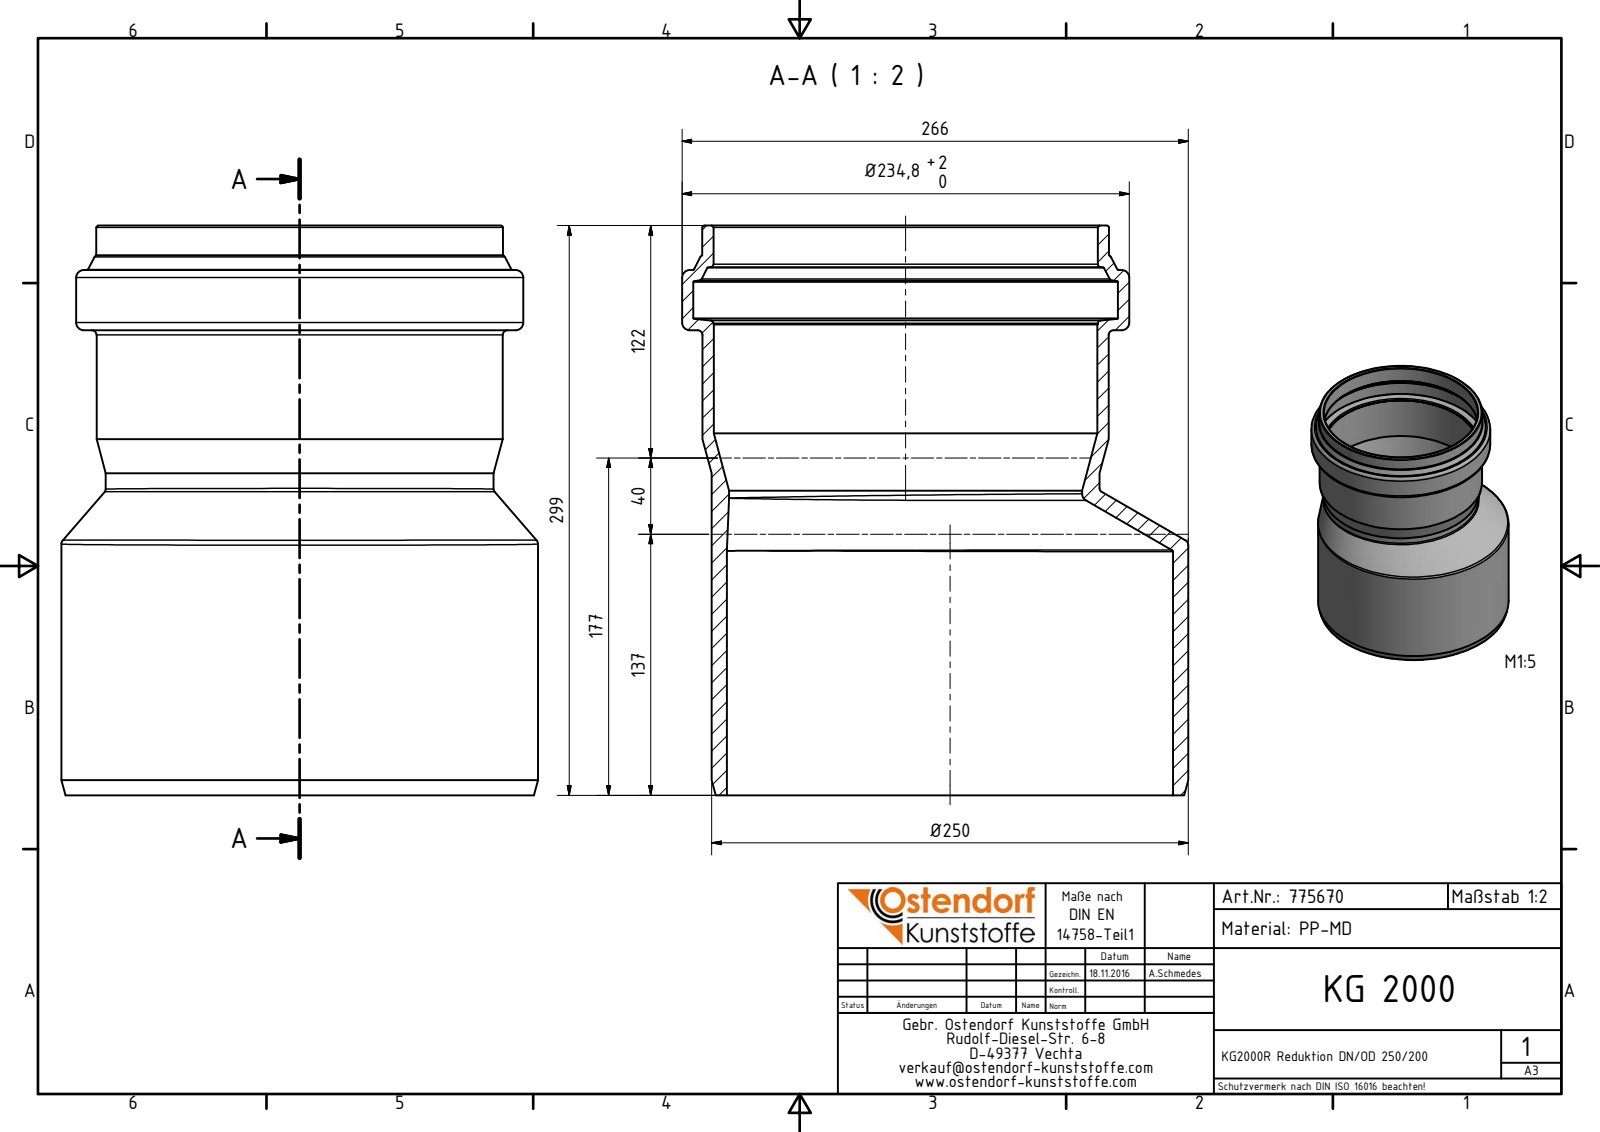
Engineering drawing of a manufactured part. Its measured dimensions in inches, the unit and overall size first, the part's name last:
Units: inches
Overall size (bounding box): 11.772 × 10.467 × 9.854
Round holes (diameter × count): ⌀7.298 ×1, ⌀7.933 ×1, ⌀7.945 ×1, ⌀8.78 ×1, ⌀9.224 ×1
Round bosses / shafts (diameter × count): ⌀9.854 ×1, ⌀9.244 ×1, ⌀8.409 ×1, ⌀8.398 ×1, ⌀8.02 ×1
Main face-to-face distances: 9.61, 11.772, 2.161, 10.854, 1.244, 0.917, 9.73, 0.119, 1.125, 2.042
Hole centre spacings: 0.917
Volume: 101.3 in³ · Surface area: 723.2 in²
Bodies: 1 solid, 44 faces (5 planar, 11 cylindrical, 28 other)
Part name (STEP PRODUCT): 775670 KG2000R Reduktion DN_OD 250_200
STEP written by: Autodesk Inventor 2016 (AUTOMOTIVE_DESIGN)
